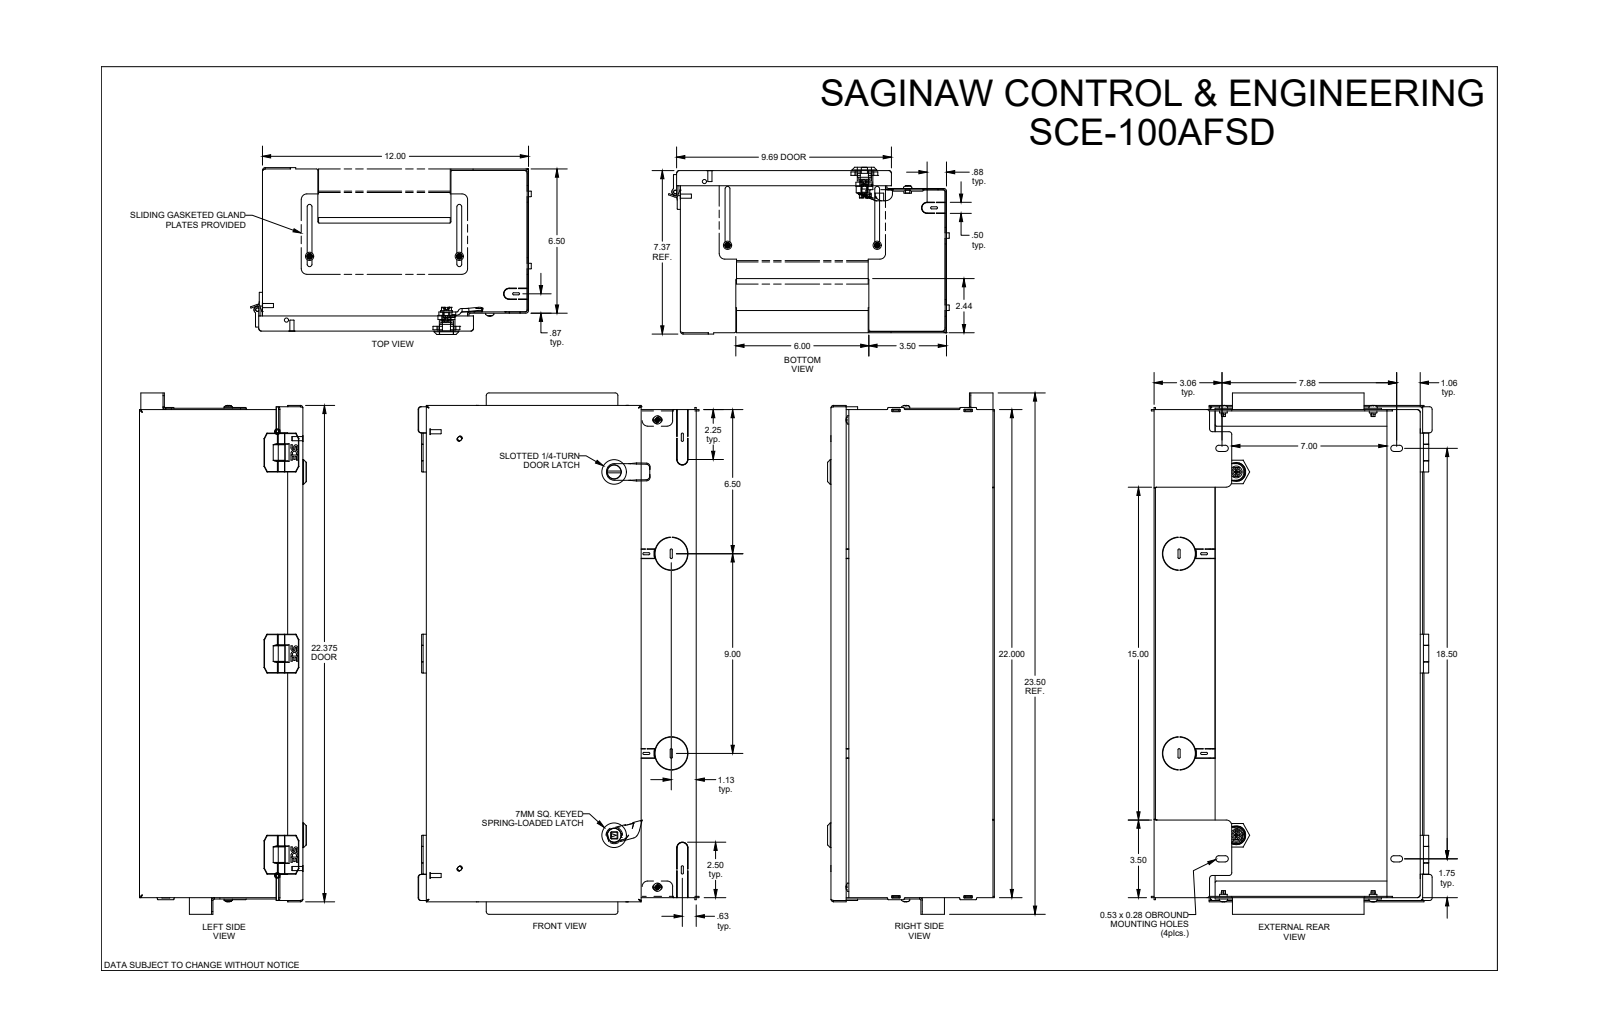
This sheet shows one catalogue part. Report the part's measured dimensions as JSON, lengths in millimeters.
{"part_name": "SCE-100AFSD", "step_written_by": "SolidWorks 2019 (AUTOMOTIVE_DESIGN)", "units": "millimeters", "bodies": {"solids": 50, "faces": 1773, "planar": 774, "cylindrical": 618, "other": 381}, "overall_size": [596.9, 321.7, 191], "volume_mm3": 1261000, "surface_area_mm2": 1481000, "round_holes": [[4.9, 4], [4.9, 2], [7.6, 2], [10.2, 2], [10.3, 2], [16.2, 2], [21.6, 2], [38.1, 2], [4, 1], [5.7, 1], [5.7, 1], [6.4, 1]], "round_bosses_or_shafts": [[6, 6], [4.1, 6], [12.7, 4], [9.5, 4], [8.7, 4], [6.6, 4], [6.2, 4], [4.8, 4]], "partial_cylinders_radius": [[0.5, 144], [0.1, 32], [0.3, 20], [0.8, 16], [6.4, 15], [3.2, 14], [1.5, 13], [2.8, 12]], "face_to_face_distances": [1.5, 3.9, 303.3, 2.4, 5.4, 558.8, 304.8, 301.8, 557.3, 16.6], "hole_center_spacings": [77.5, 114.3, 154, 181, 227.6, 275.9, 328.9, 382.1]}
